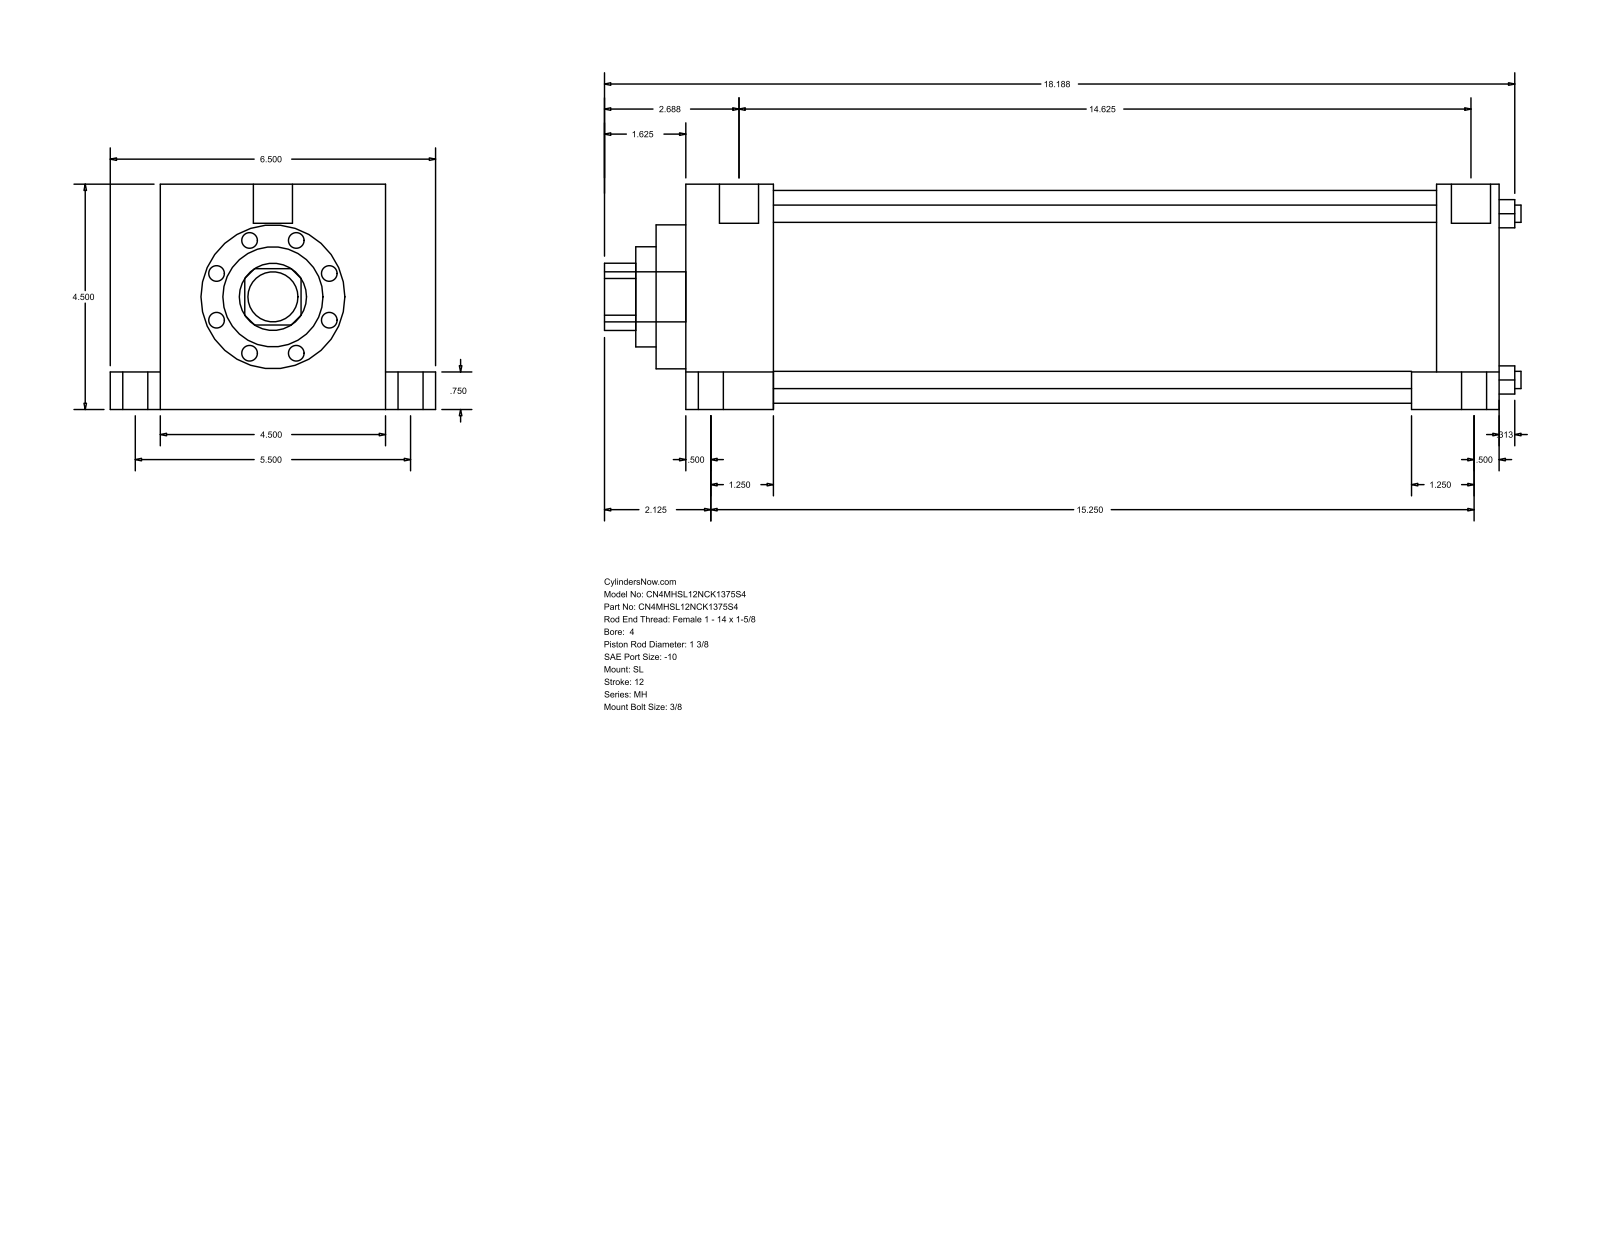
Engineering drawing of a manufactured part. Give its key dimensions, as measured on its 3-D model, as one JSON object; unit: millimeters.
{"part_name": "MH_SL__0400_1.375", "step_written_by": "GSSL Pune (CONFIG_CONTROL_DESIGN)", "units": "millimeters", "bodies": {"solids": 0, "faces": 110, "planar": 77, "cylindrical": 33, "other": 0}, "overall_size": [465.14, 165.1, 114.3], "round_holes": [[8.76, 4], [34.92, 1], [50.8, 1], [73.03, 1], [107.95, 1]], "round_bosses_or_shafts": [[19.05, 4], [12.7, 4], [8.73, 4], [19.84, 2], [25.4, 1]], "partial_cylinders_radius": [[17.06, 1]], "face_to_face_distances": [114.3, 412.75, 44.45, 368.3, 381, 336.55, 31.75, 25.4, 139.7, 19.05], "hole_center_spacings": [59.62, 84.32, 119.25]}
